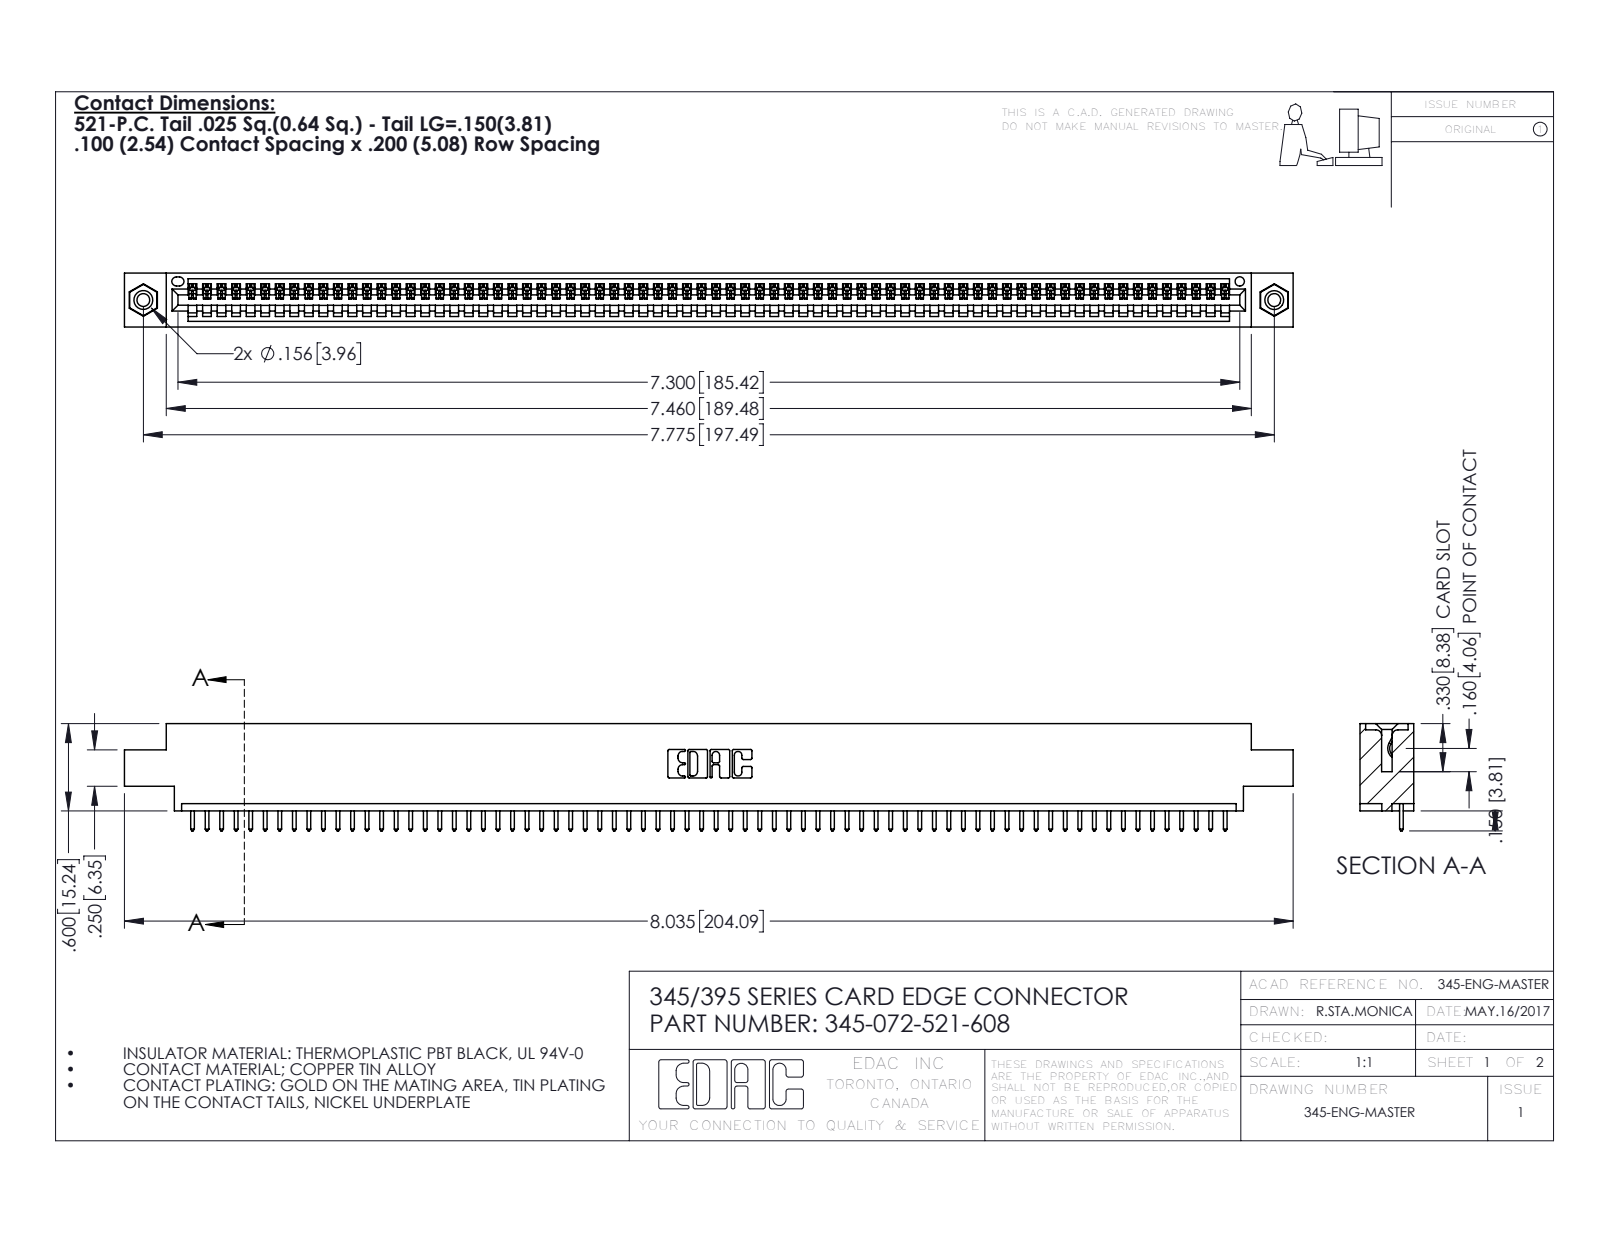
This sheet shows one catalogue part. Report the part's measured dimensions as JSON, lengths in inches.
{"part_name": "345 Part_0.170 Offset - 0.156 Dia-TI; 345-292-001_345-293-121; 345-072-521-608; 345-250-001_345-250-003-102", "step_written_by": "SolidWorks 2016 (CONFIG_CONTROL_DESIGN)", "units": "inches", "bodies": {"solids": 75, "faces": 4366, "planar": 2996, "cylindrical": 1354, "other": 16}, "overall_size": [8.035, 0.737, 0.37], "volume_in3": 1.178, "surface_area_in2": 39.38, "round_holes": [[0.089, 2], [0.125, 2], [0.156, 2], [0.064, 1]], "round_bosses_or_shafts": [[0.155, 2]], "partial_cylinders_radius": [[0.006, 144], [0.01, 144], [0.01, 22], [0.007, 6], [0.031, 6], [0.026, 3], [0.031, 2], [0.04, 2]], "face_to_face_distances": [0.072, 0.298, 0.37, 0.2, 0.098, 0.272, 0.025, 0.225, 0.149, 0.175], "hole_center_spacings": [0.27, 7.539, 7.775]}
